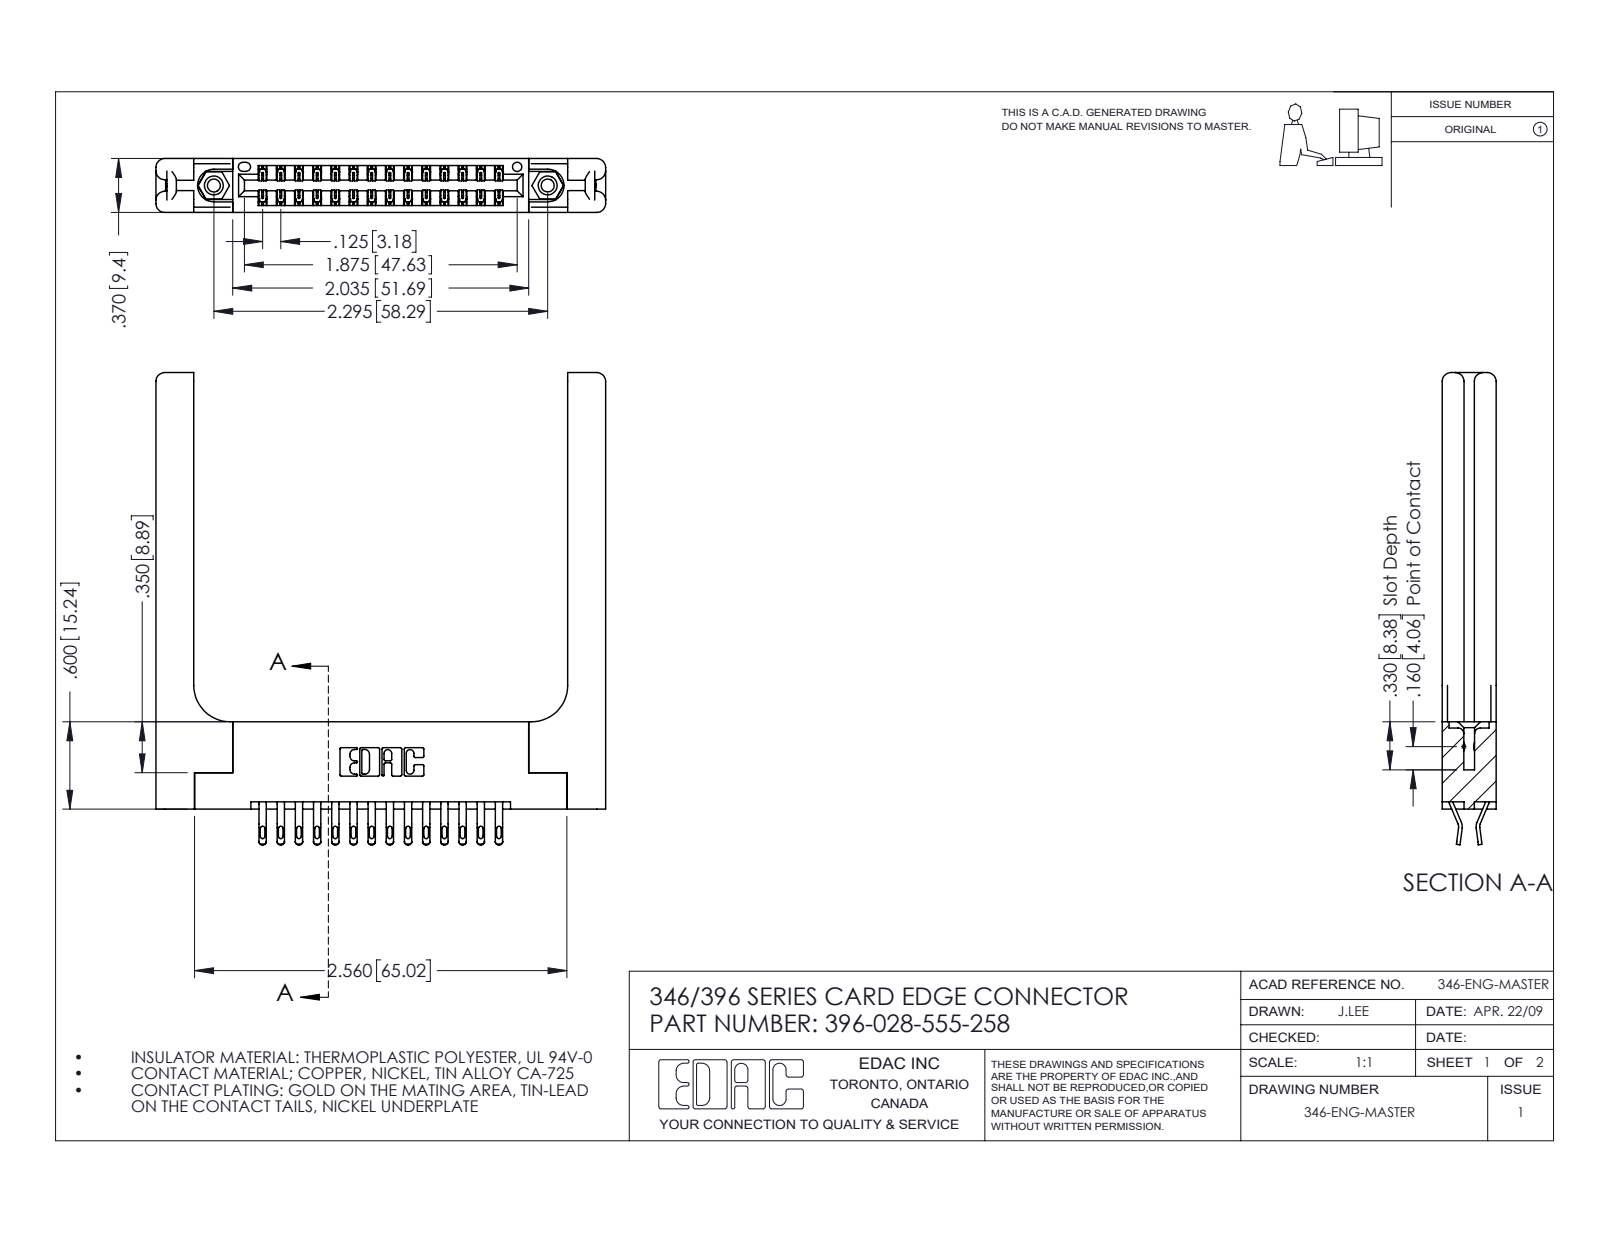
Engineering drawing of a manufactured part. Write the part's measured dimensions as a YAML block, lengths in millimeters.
part_name: "345-292-001_555 Tail; 346 Part_Flush Mounting Lugs - 0.156 Dia-TH; 346-220-058_345-220-058; 345-250-001_345-250-001-102 (+1 more)"
step_written_by: "SolidWorks 2016 (CONFIG_CONTROL_DESIGN)"
units: millimeters
bodies: {solids: 33, faces: 2002, planar: 1148, cylindrical: 794, other: 60}
overall_size: [82.4, 78.5, 9.4]
volume: 15000
surface_area: 15160
round_holes:
  - {diameter: 2.3, count: 2}
  - {diameter: 3.2, count: 2}
  - {diameter: 4, count: 2}
  - {diameter: 1.6, count: 1}
round_bosses_or_shafts:
  - {diameter: 3.9, count: 2}
partial_cylinders:
  - {radius: 0.4, count: 56}
  - {radius: 0.5, count: 56}
  - {radius: 0.2, count: 42}
  - {radius: 0.3, count: 22}
  - {radius: 1.5, count: 16}
  - {radius: 0.2, count: 6}
  - {radius: 0.8, count: 6}
  - {radius: 0.7, count: 3}
face_to_face_distances: [9.4, 3.8, 1.8, 3.8, 1.2, 8.2, 6.4, 2.6, 5.6, 4.4]
hole_center_spacings: [6.2, 53.1, 58.3]
